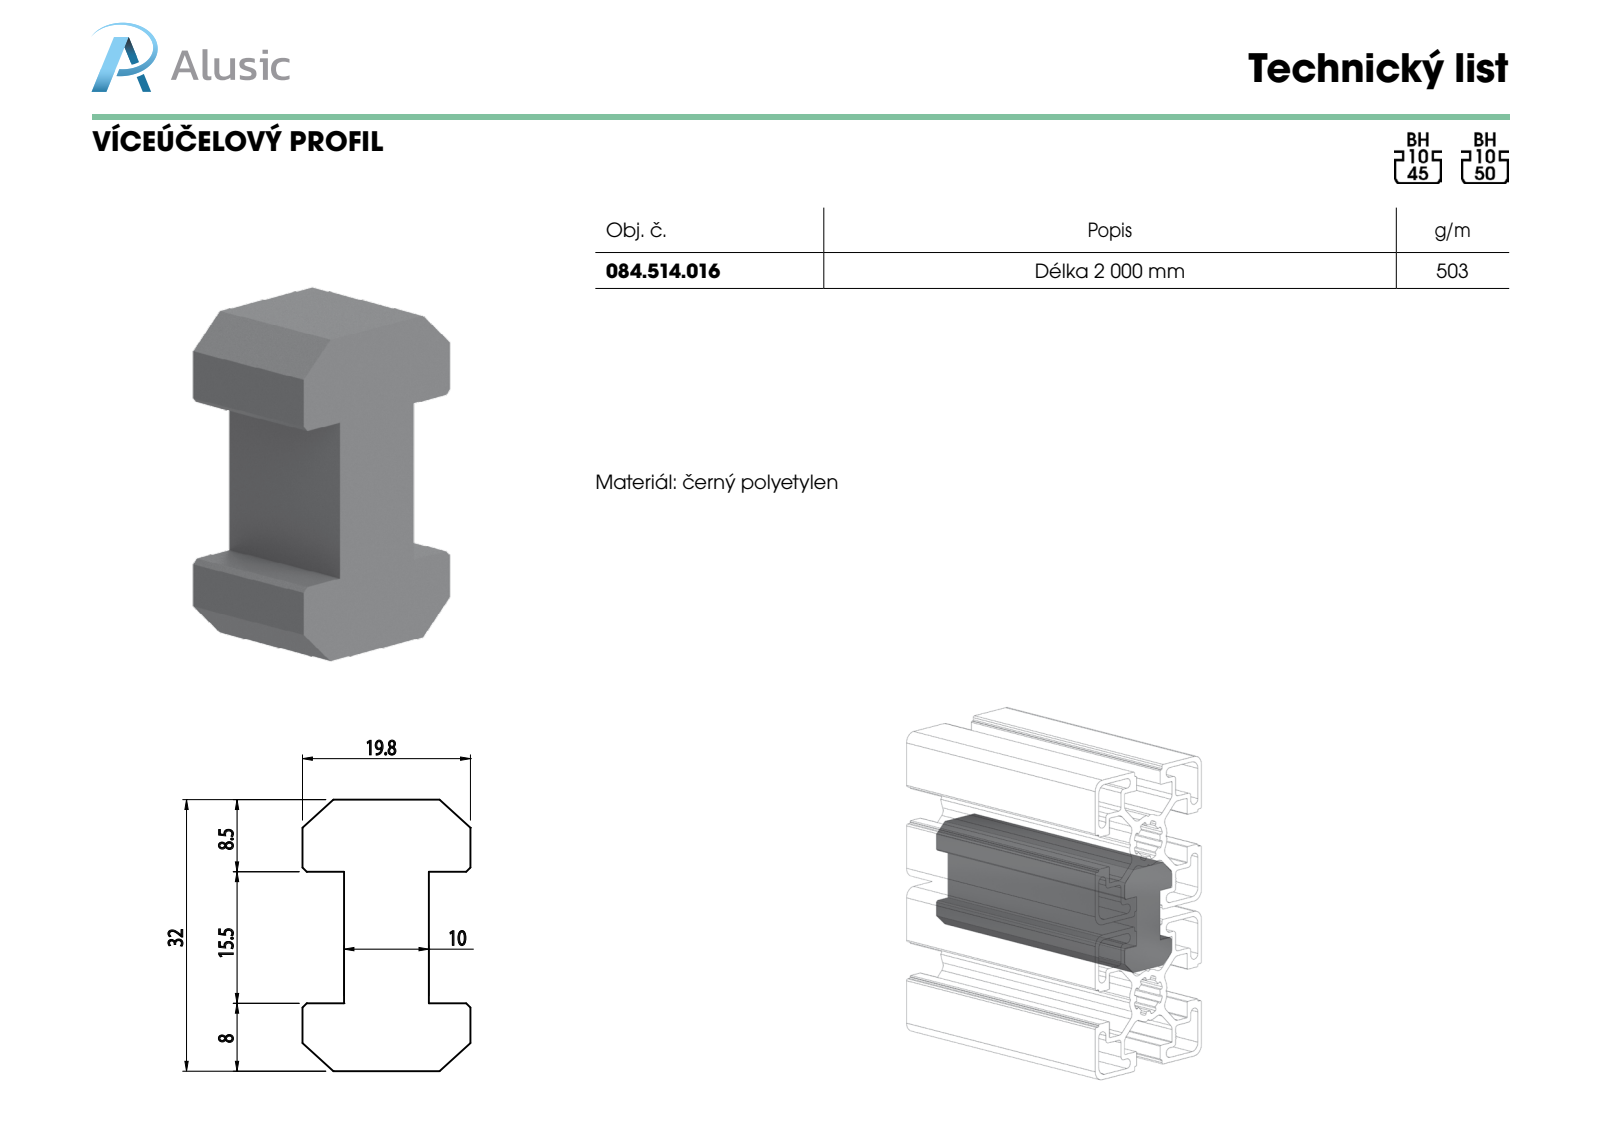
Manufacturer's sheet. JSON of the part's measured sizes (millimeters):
{"part_name": "084.514.016", "step_written_by": "SolidWorks 2012 (CONFIG_CONTROL_DESIGN)", "units": "millimeters", "bodies": {"solids": 1, "faces": 22, "planar": 22, "cylindrical": 0, "other": 0}, "overall_size": [100, 32, 19.8], "volume_mm3": 45708, "surface_area_mm2": 12305, "face_to_face_distances": [4.9, 14.9, 10, 32, 32.1, 19.8, 8, 23.5, 15.5, 24]}
